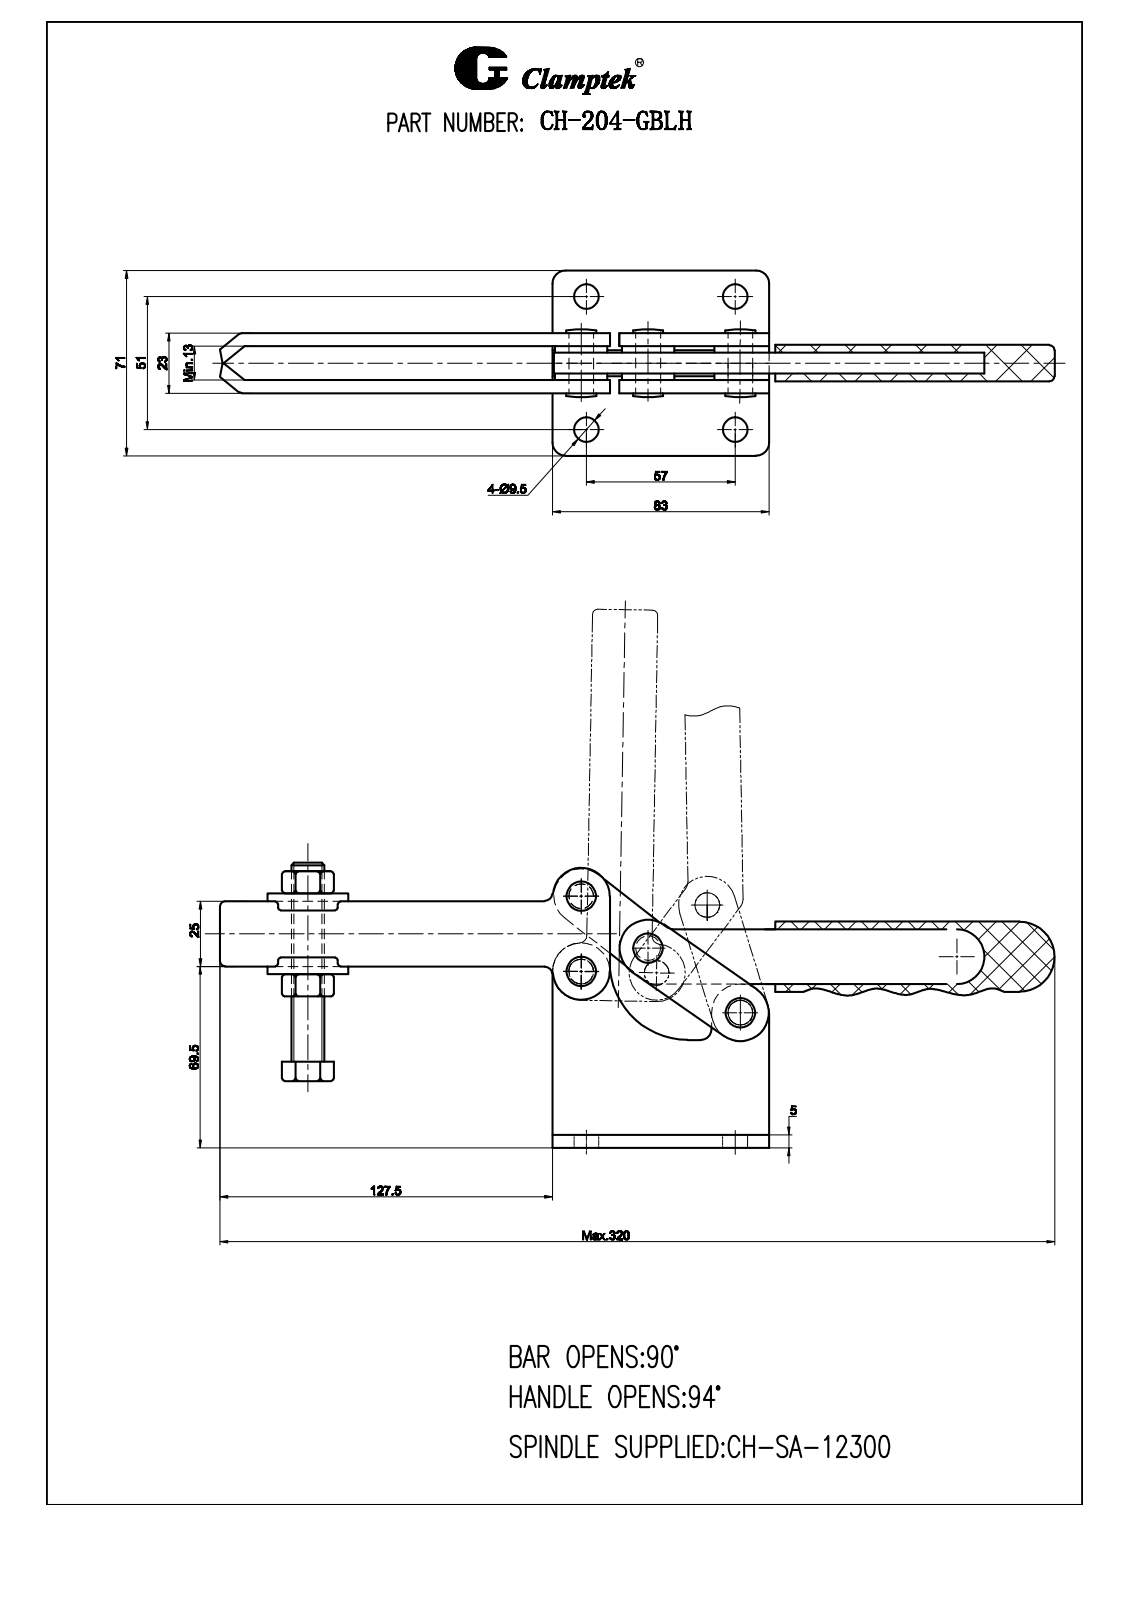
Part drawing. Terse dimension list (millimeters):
name: 204-GB-07; 204-GB-03; 204-GBLH-02; 204-GB-06 (+8 more)
written by: SolidWorks 2010 (CONFIG_CONTROL_DESIGN)
unit: mm
bodies: 25 solids, 1671 faces (572 planar, 450 cylindrical, 649 other)
size: 315.23 × 144.83 × 71
volume: 206 897 mm³; area: 108 132 mm²
holes: 8× ⌀9.5, 4× ⌀10, 2× ⌀10.2, 2× ⌀10.5, 1× ⌀4
bosses: 4× ⌀20, 4× ⌀12, 4× ⌀9.4, 2× ⌀22, 1× ⌀12.7, 1× ⌀2.8
rounds: 84× R0.25, 9× R5, 8× R25.91, 7× R3.5, 6× R3, 4× R10, 3× R4.5, 2× R8.6
face distances: 6.5, 5, 11.5, 4, 2.5, 10.5, 18, 7.5, 15.5, 9
hole spacings: 51, 57, 76.48, 27.47, 28.91, 32.51, 43.2, 63
